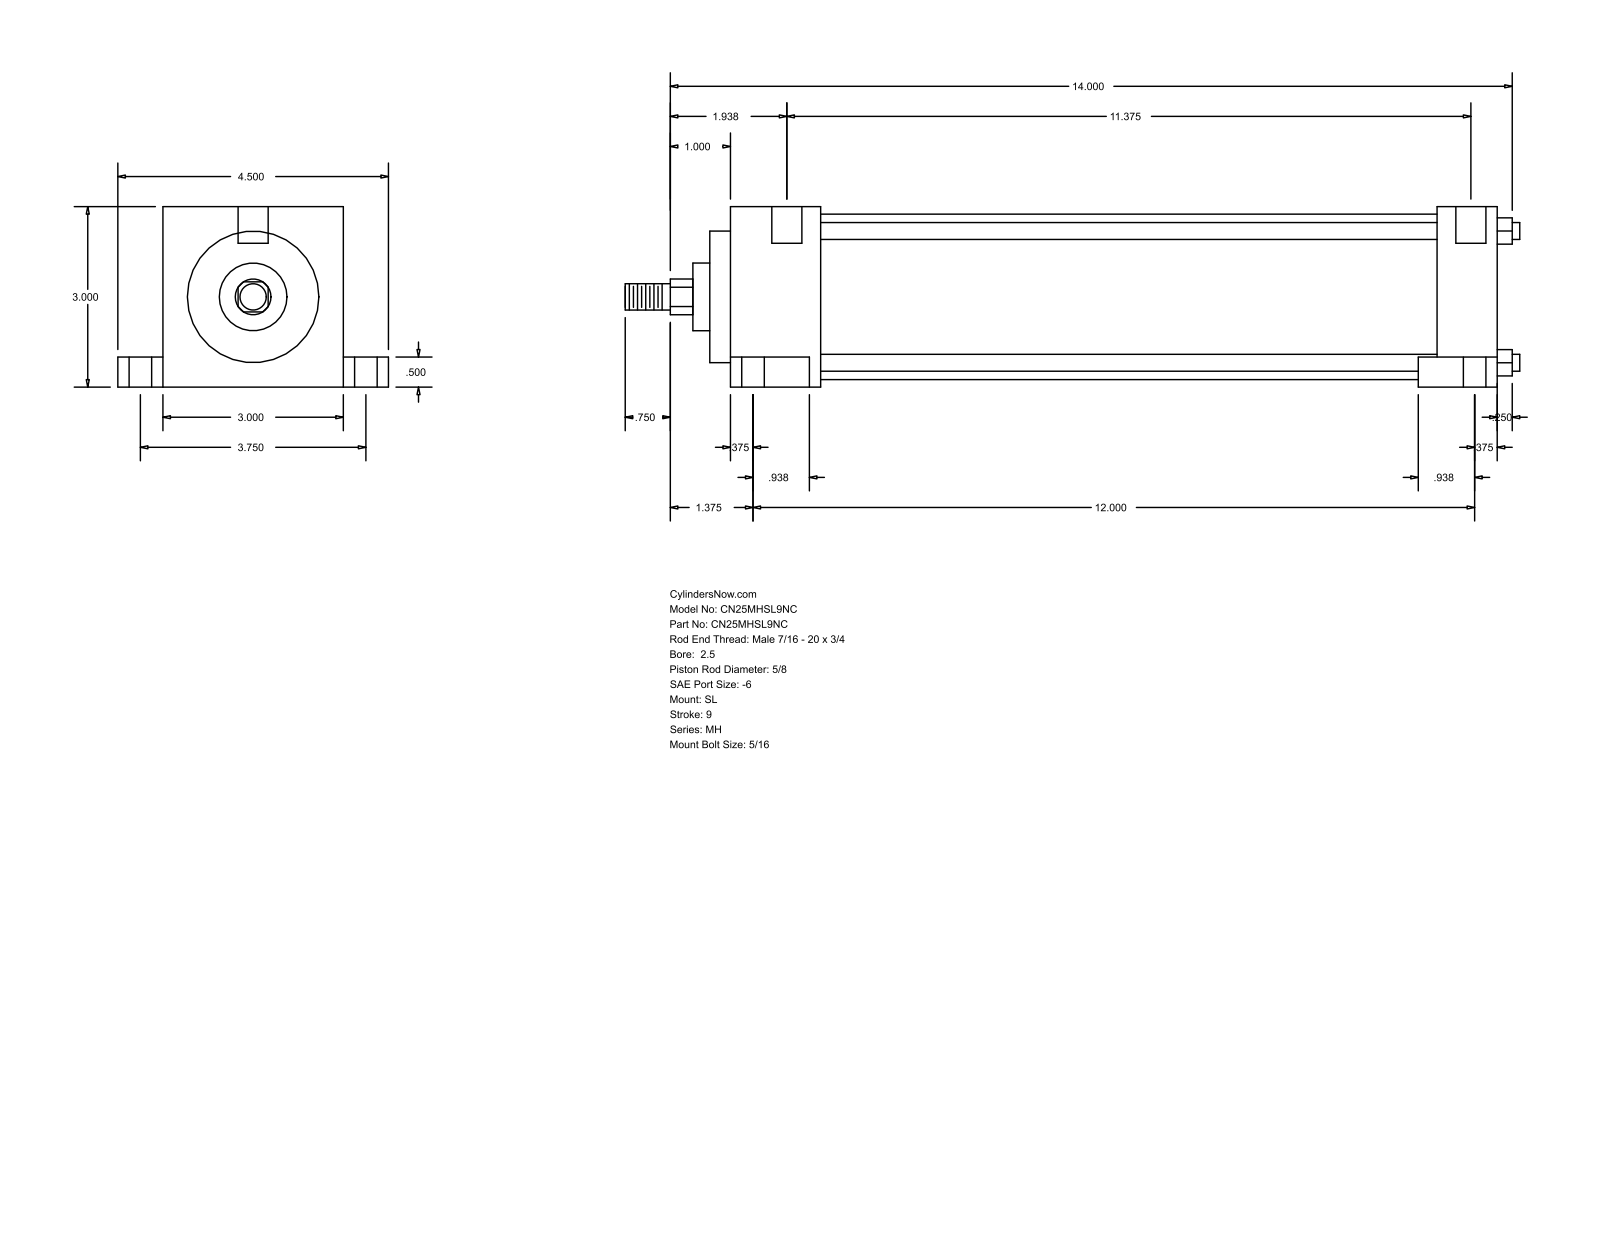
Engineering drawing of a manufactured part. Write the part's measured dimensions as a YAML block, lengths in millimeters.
part_name: "MH_SL__0250_0.625"
step_written_by: "GSSL Pune (CONFIG_CONTROL_DESIGN)"
units: millimeters
bodies: {solids: 0, faces: 86, planar: 61, cylindrical: 25, other: 0}
overall_size: [377.82, 114.3, 76.2]
round_holes:
  - {diameter: 5.56, count: 2}
  - {diameter: 9.53, count: 2}
  - {diameter: 15.88, count: 2}
  - {diameter: 12.7, count: 1}
round_bosses_or_shafts:
  - {diameter: 7.14, count: 4}
  - {diameter: 69.85, count: 1}
  - {diameter: 55.55, count: 1}
  - {diameter: 28.57, count: 1}
  - {diameter: 15.88, count: 1}
  - {diameter: 11.11, count: 1}
partial_cylinders:
  - {radius: 7.54, count: 1}
face_to_face_distances: [76.2, 25.4, 307.18, 332.58, 63.5, 12.7, 19.05, 95.25, 31.75, 299.24]
hole_center_spacings: [47.65, 3.17, 95.24]
